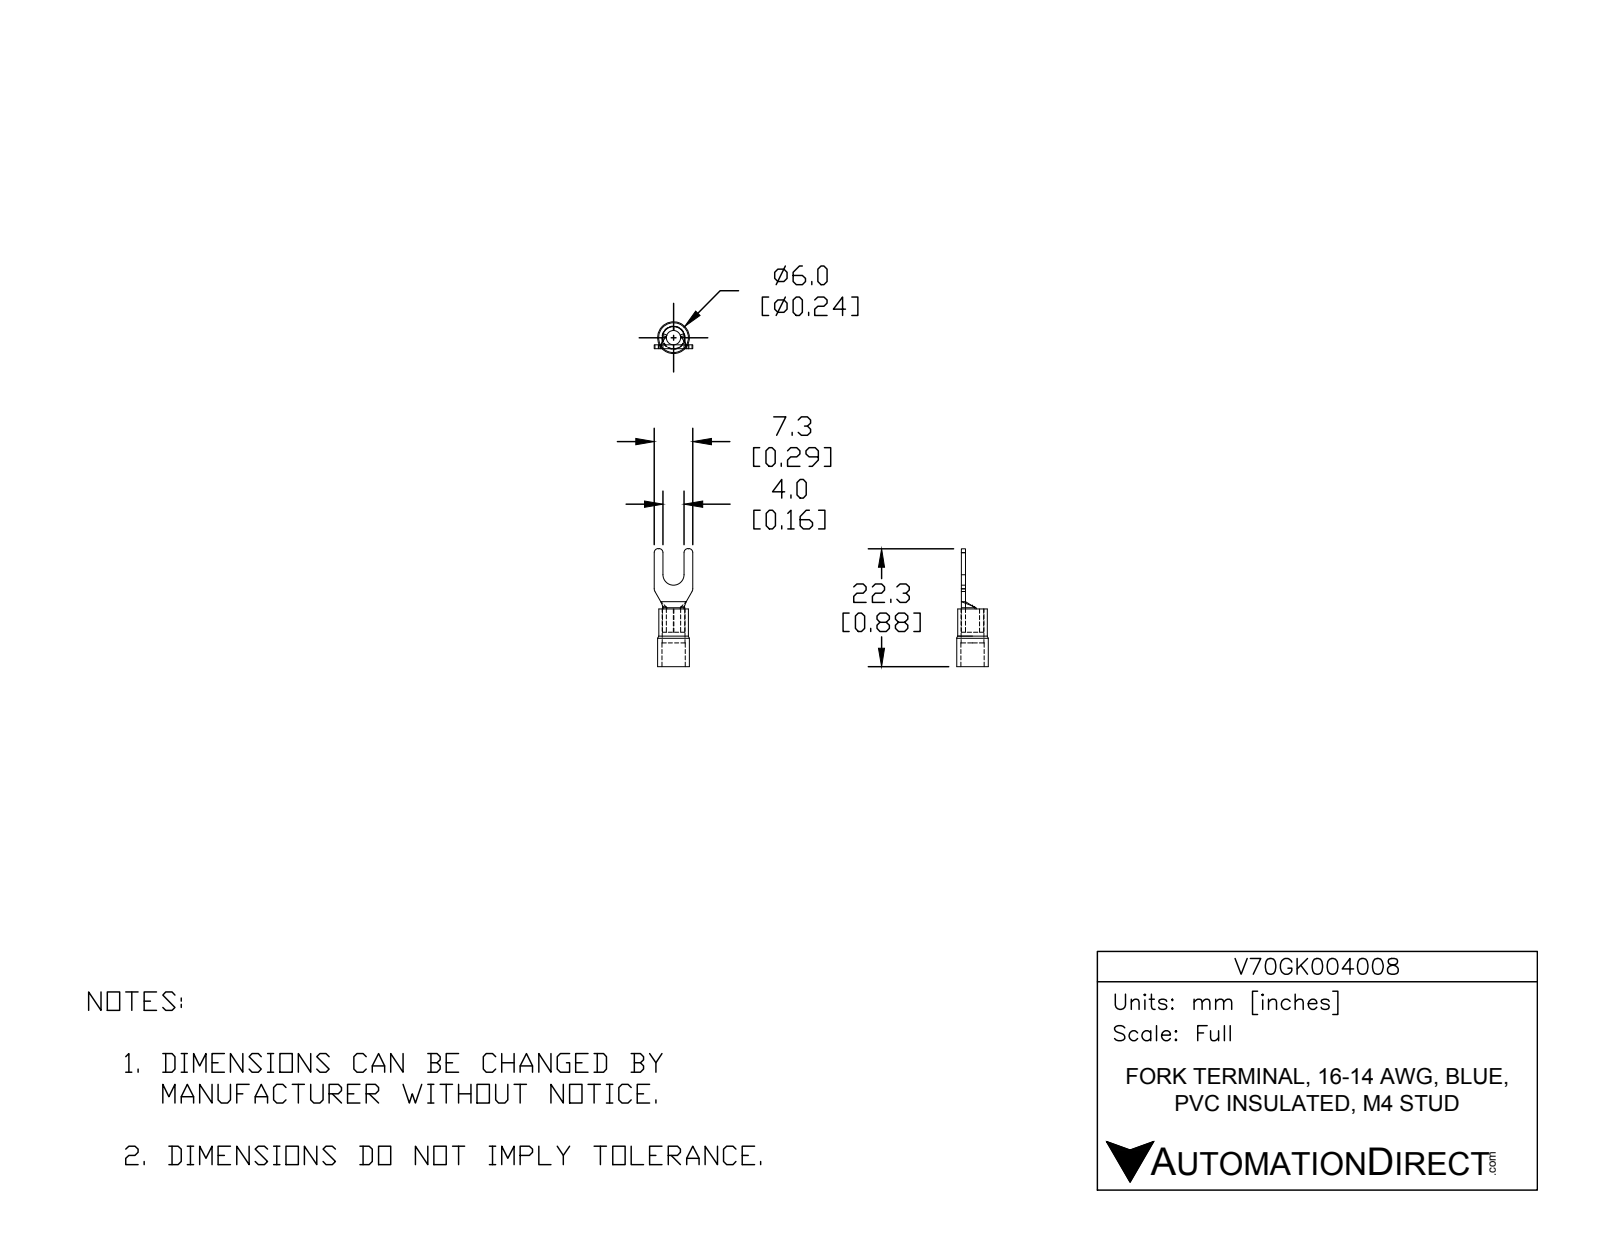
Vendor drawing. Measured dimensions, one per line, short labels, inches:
name: V70GK004008
written by: SolidWorks 2017 (AUTOMOTIVE_DESIGN)
unit: in
bodies: 2 solids, 47 faces (18 planar, 21 cylindrical, 8 other)
size: 0.878 × 0.287 × 0.236
volume: 0.012 in³; area: 0.963 in²
holes: 1× ⌀0.106, 1× ⌀0.169, 1× ⌀0.173
bosses: 1× ⌀0.236, 1× ⌀0.22, 1× ⌀0.165
rounds: 4× R0.03, 2× R0.039, 1× R0.079
face distances: 0.03, 0.429, 0.256, 0.173, 0.142, 0.146, 0.065, 0.222, 0.077, 0.081
